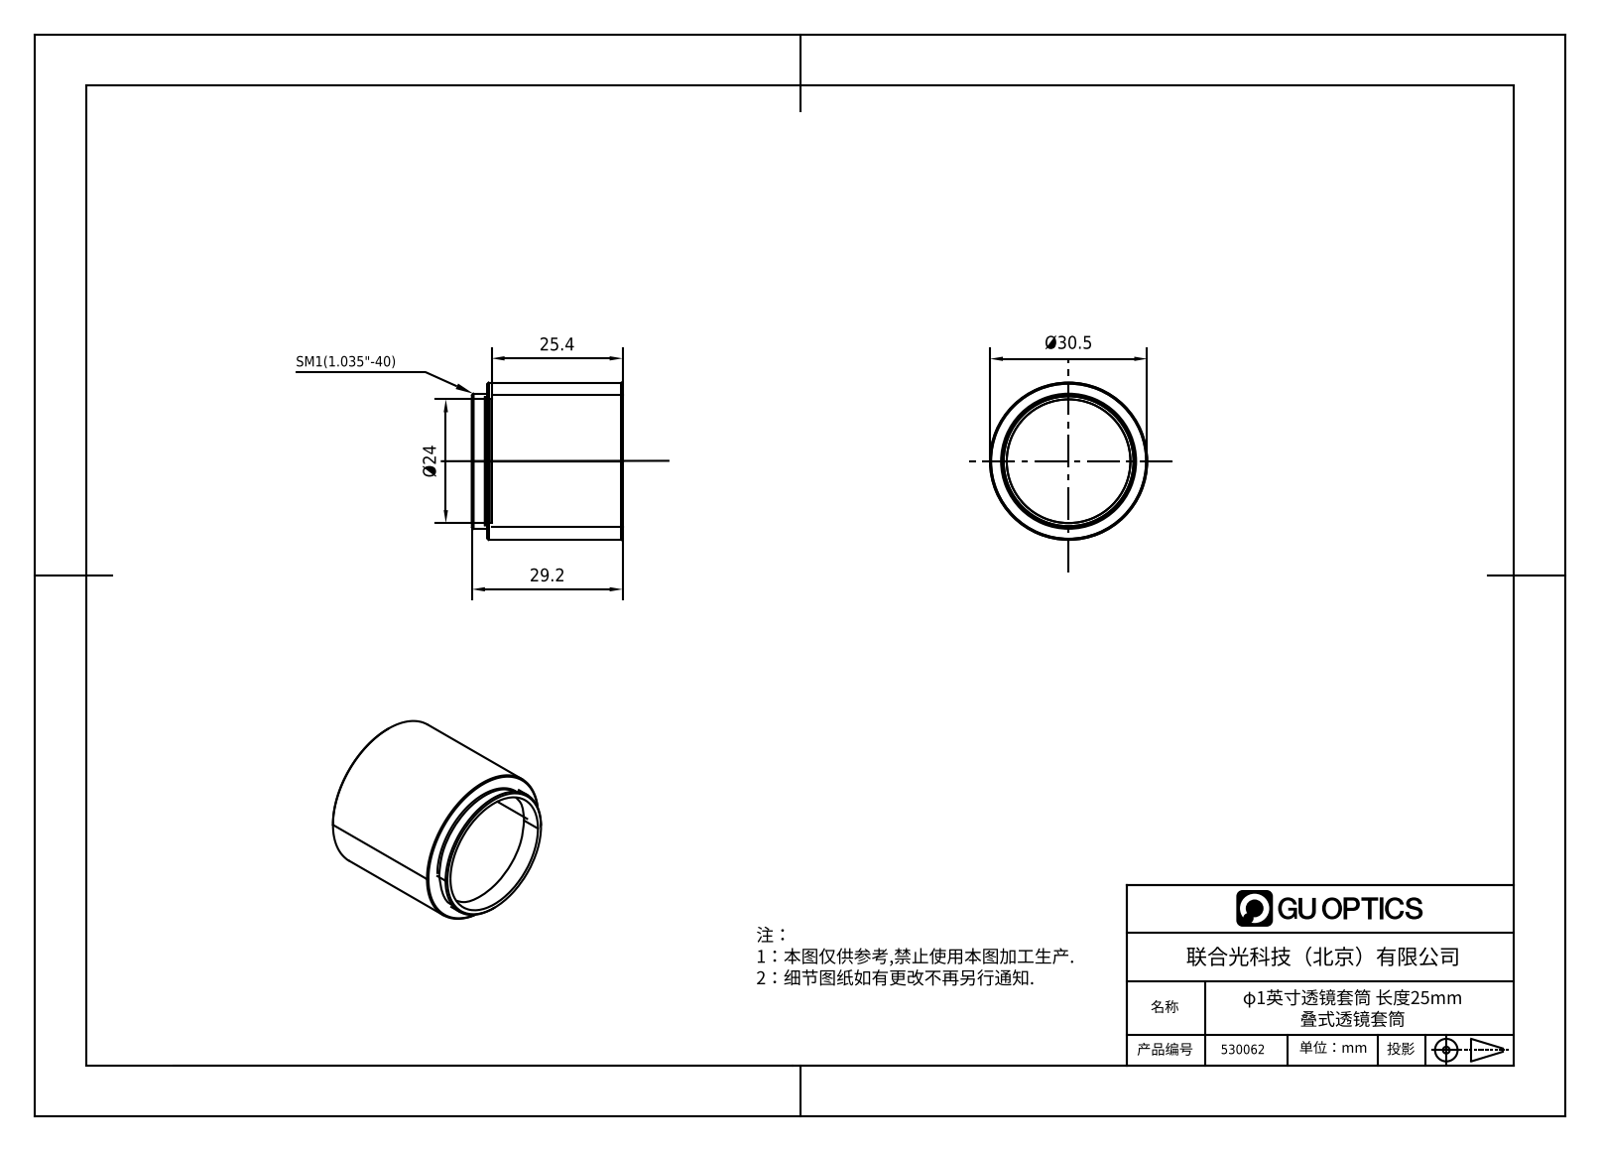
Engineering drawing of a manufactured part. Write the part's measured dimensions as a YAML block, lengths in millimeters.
part_name: "1.7.1.9_ZTC-1-1.0_SM1标准型1.0英寸层叠式透镜套筒"
step_written_by: "SolidWorks 2018 (AUTOMOTIVE_DESIGN)"
units: millimeters
bodies: {solids: 0, faces: 34, planar: 11, cylindrical: 12, other: 11}
overall_size: [30.5, 30.5, 29.2]
round_holes:
  - {diameter: 23.01, count: 1}
  - {diameter: 24, count: 1}
  - {diameter: 25.65, count: 1}
round_bosses_or_shafts:
  - {diameter: 30.5, count: 1}
  - {diameter: 26.2, count: 1}
  - {diameter: 25.2, count: 1}
face_to_face_distances: [26.2, 1, 25.2, 29.2, 28.2, 3, 1.7, 0.7, 24.5, 27.5]
